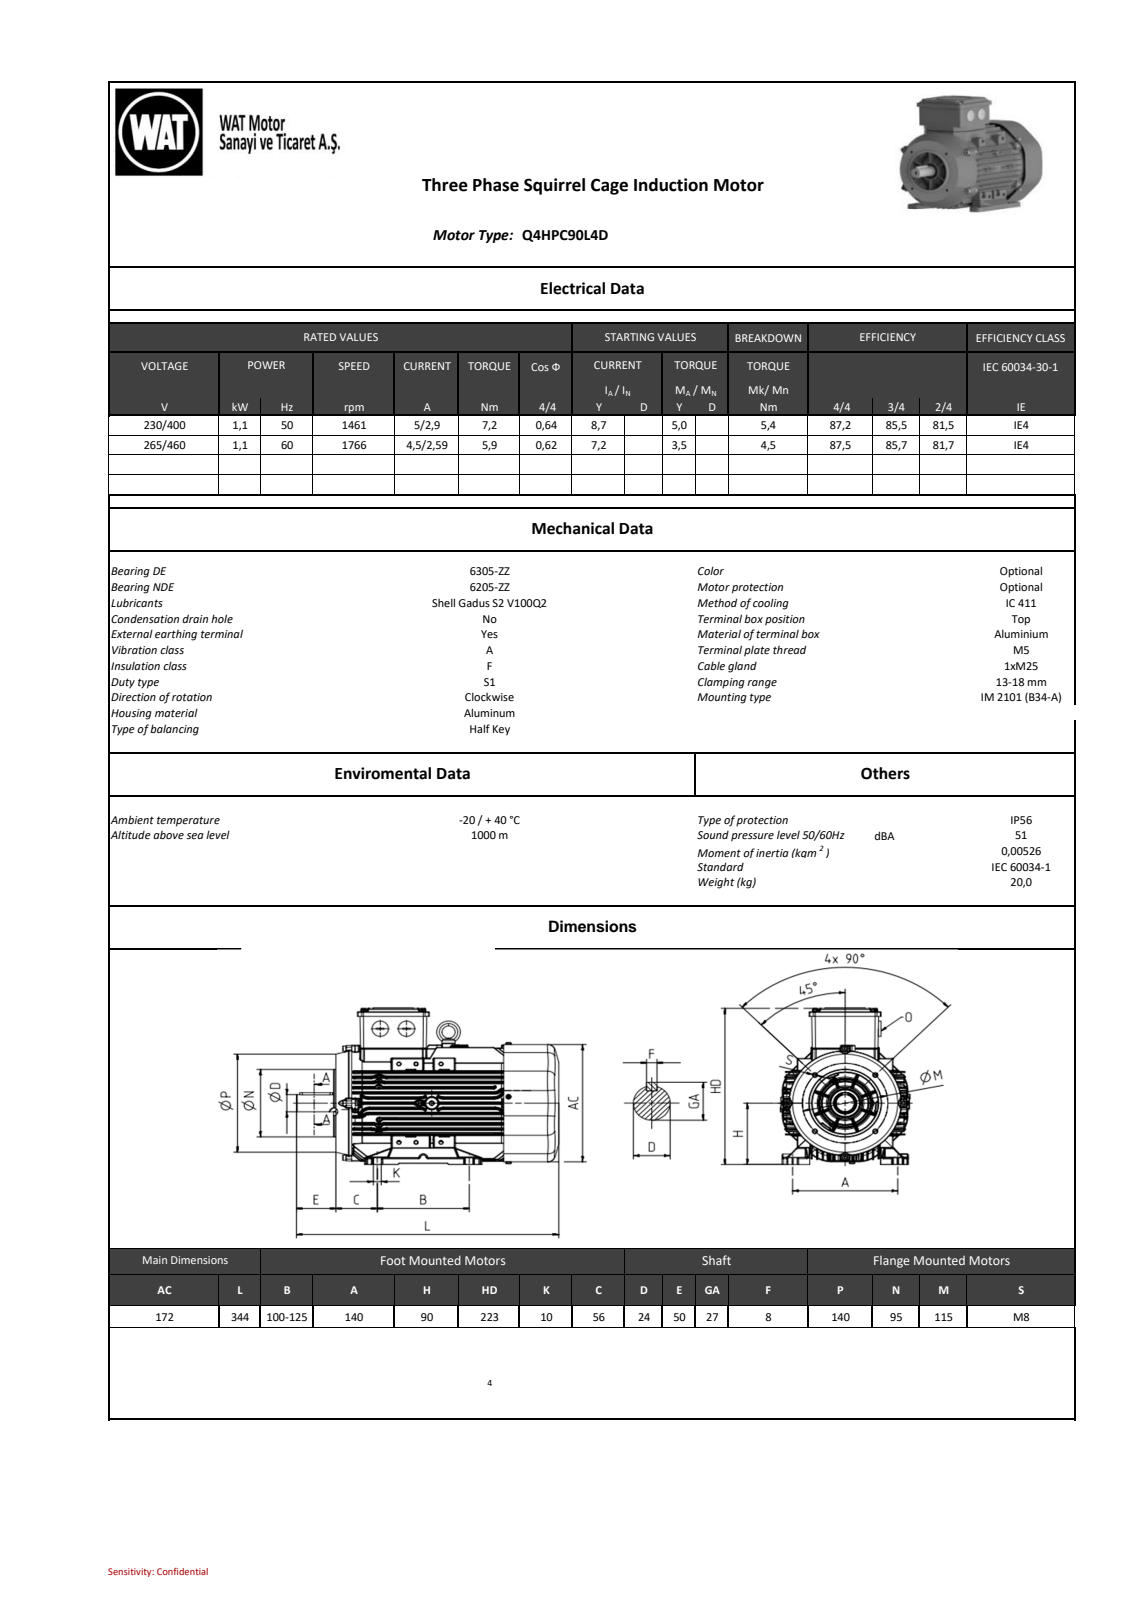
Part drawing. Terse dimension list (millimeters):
name: model1
written by: SIEMENS PLM Software NX2206.8101 (AUTOMOTIVE_DESIGN)
unit: mm
bodies: 0 solids, 6525 faces (1526 planar, 2789 cylindrical, 2210 other)
size: 343.54 × 223.05 × 178.35
holes: 4× ⌀6.8, 1× ⌀9.87, 1× ⌀37.42, 1× ⌀79.79, 1× ⌀97.79, 1× ⌀115.78
bosses: 8× ⌀5, 7× ⌀8, 5× ⌀10, 3× ⌀25, 1× ⌀102.19, 1× ⌀95, 1× ⌀84.19, 1× ⌀39.5
rounds: 857× R1, 543× R0.8, 107× R0.98, 78× R2, 72× R0.5, 48× R0.5, 28× R1.5, 28× R8
face distances: 7.5, 91.91, 8.93, 82.98, 23.57, 50.35, 7.37, 9.06, 90.35, 75.04
hole spacings: 57.42, 57.59, 81.32, 81.33, 115.01, 57.45, 57.46, 57.55
